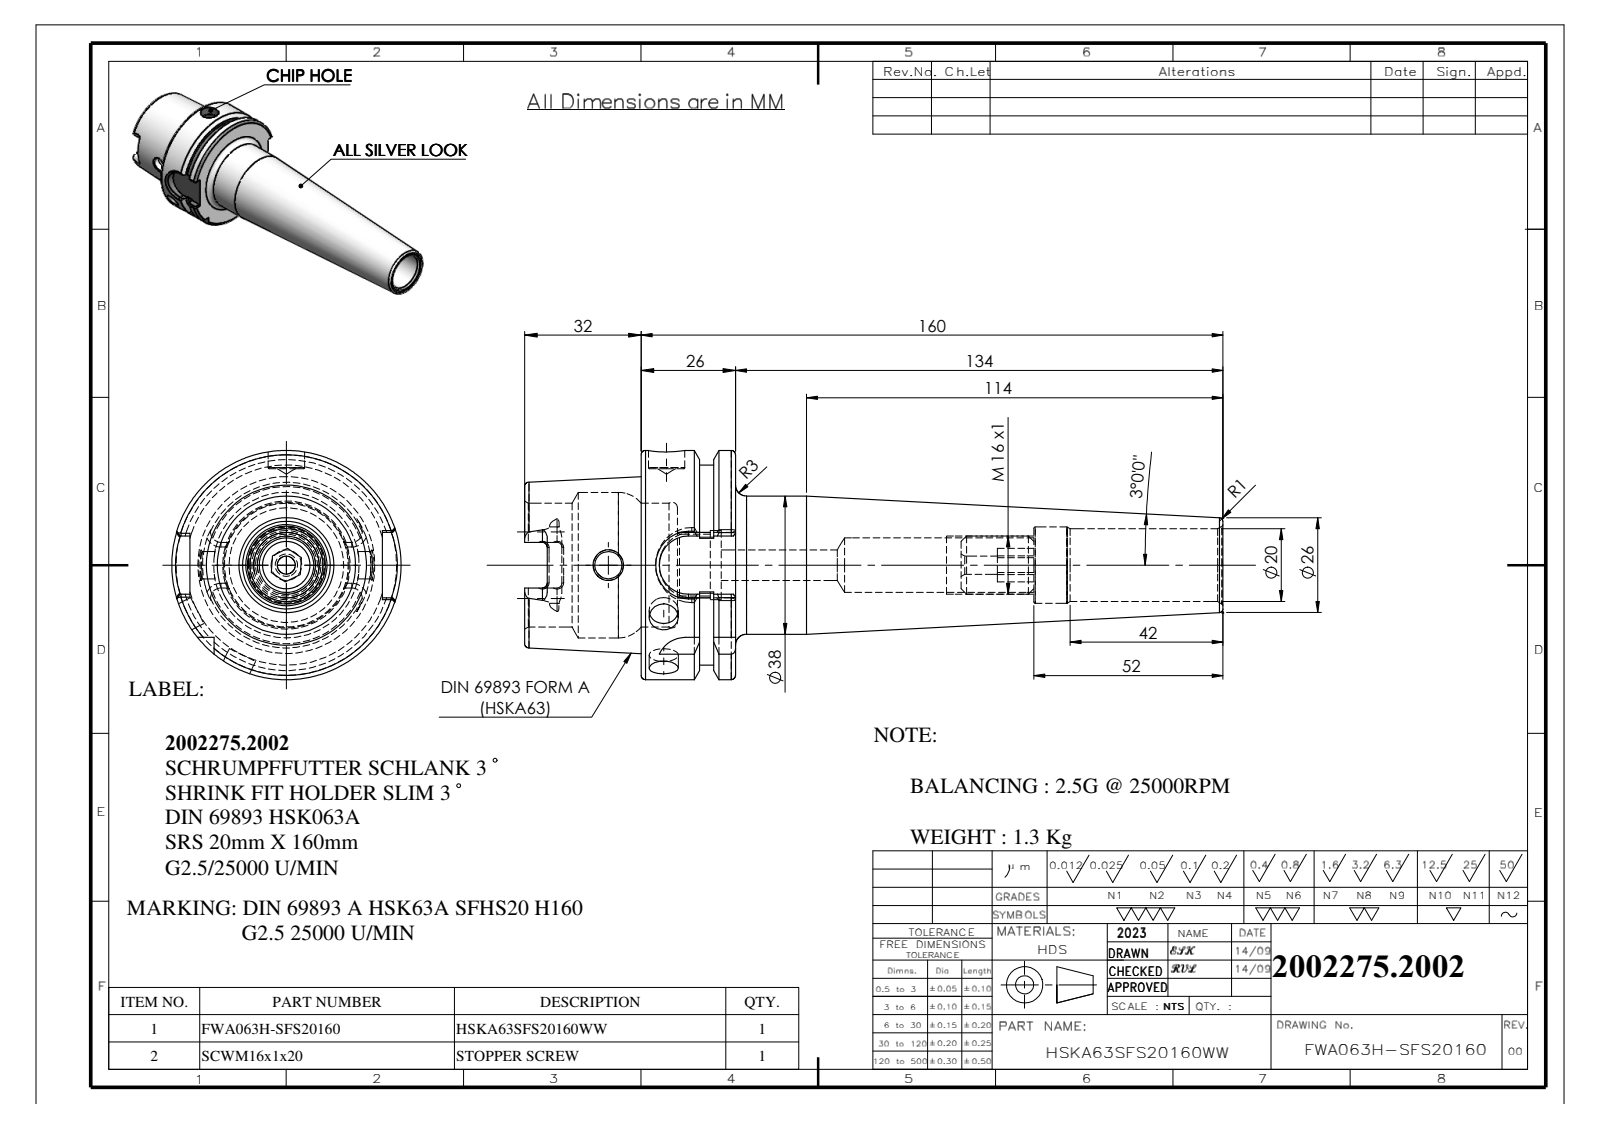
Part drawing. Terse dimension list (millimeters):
name: HSKA63SFS20160WW; SCWM16X1P; 9163A-SRS20160
written by: SolidWorks 2018 (CONFIG_CONTROL_DESIGN)
unit: mm
bodies: 2 solids, 196 faces (59 planar, 57 cylindrical, 80 other)
size: 191.95 × 63 × 63
volume: 171 832 mm³; area: 43 607 mm²
holes: 2× ⌀8, 1× ⌀5, 1× ⌀7.5, 1× ⌀8.4, 1× ⌀10, 1× ⌀15, 1× ⌀17, 1× ⌀19, 1× ⌀20, 1× ⌀21, 1× ⌀34, 1× ⌀40
bosses: 1× ⌀63, 1× ⌀55, 1× ⌀38, 1× ⌀16
rounds: 6× R1.3, 4× R2.88, 2× R8, 1× R9
face distances: 25.95, 10, 15.95, 32, 42, 57.95, 52.9, 97.95, 54, 22
